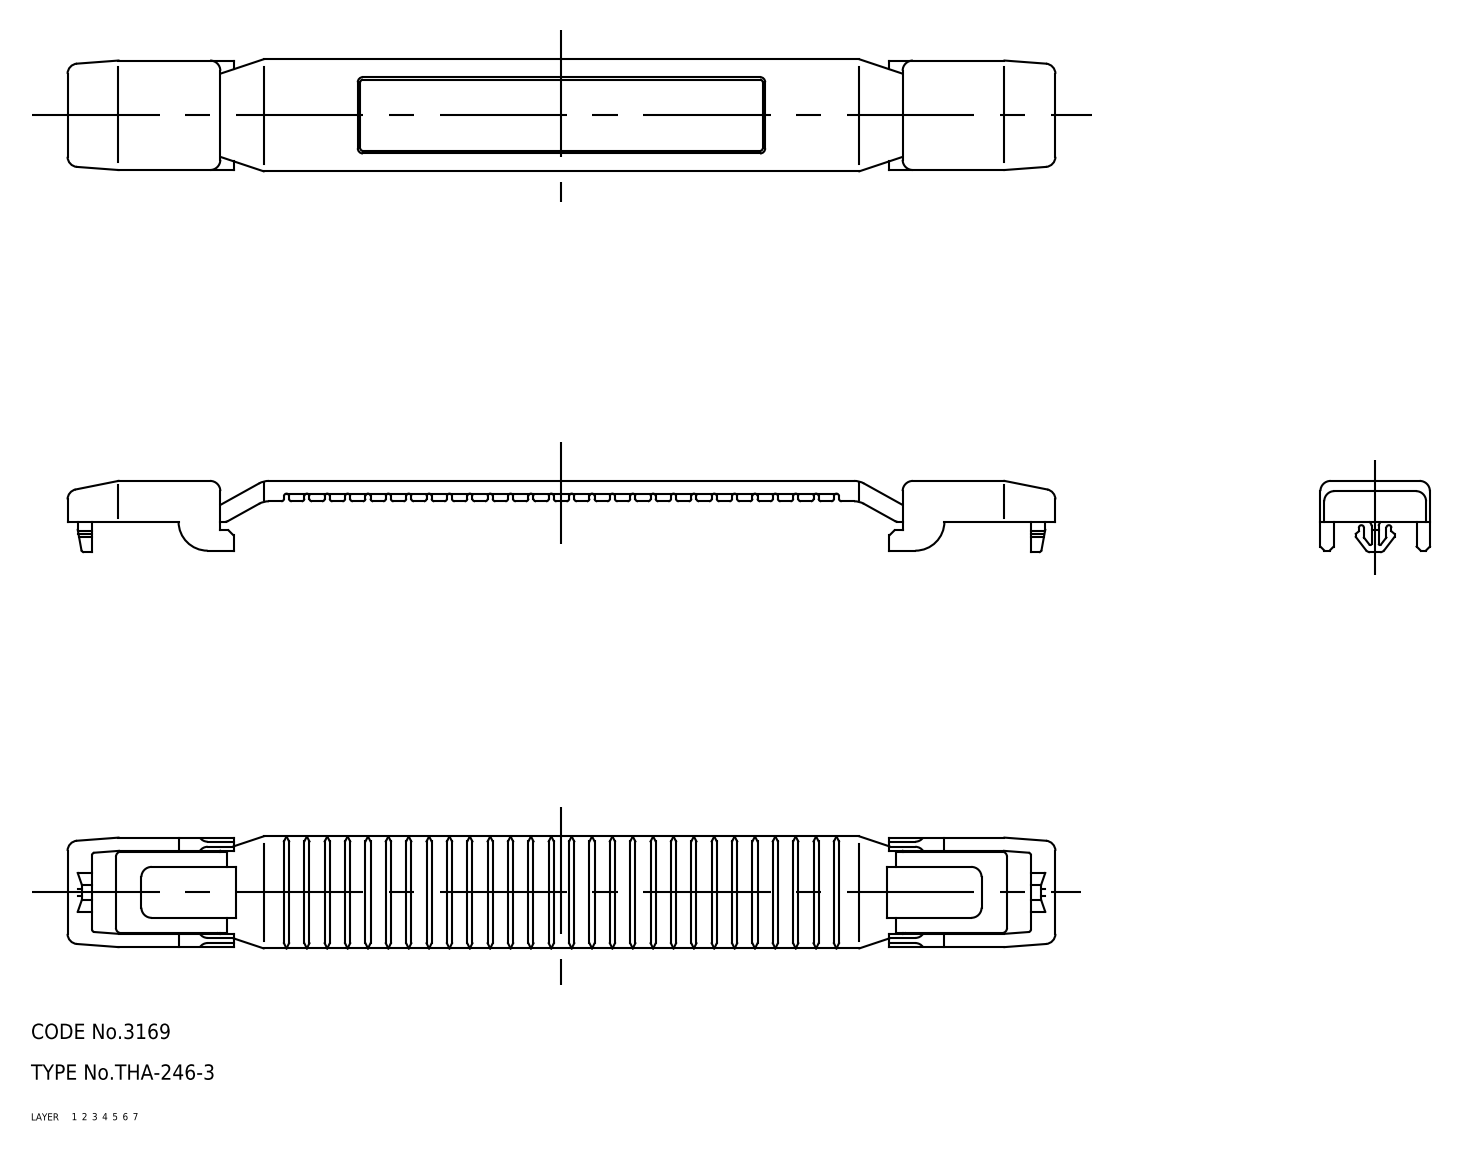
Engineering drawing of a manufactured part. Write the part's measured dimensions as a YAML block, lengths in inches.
part_name: "bracket; grip; THA_246_3_27963_36"
step_written_by: "CADfix (AUTOMOTIVE_DESIGN)"
units: inches
bodies: {solids: 3, faces: 507, planar: 0, cylindrical: 0, other: 507}
overall_size: [7.638, 0.866, 0.551]
volume: 1.091
surface_area: 22.98
